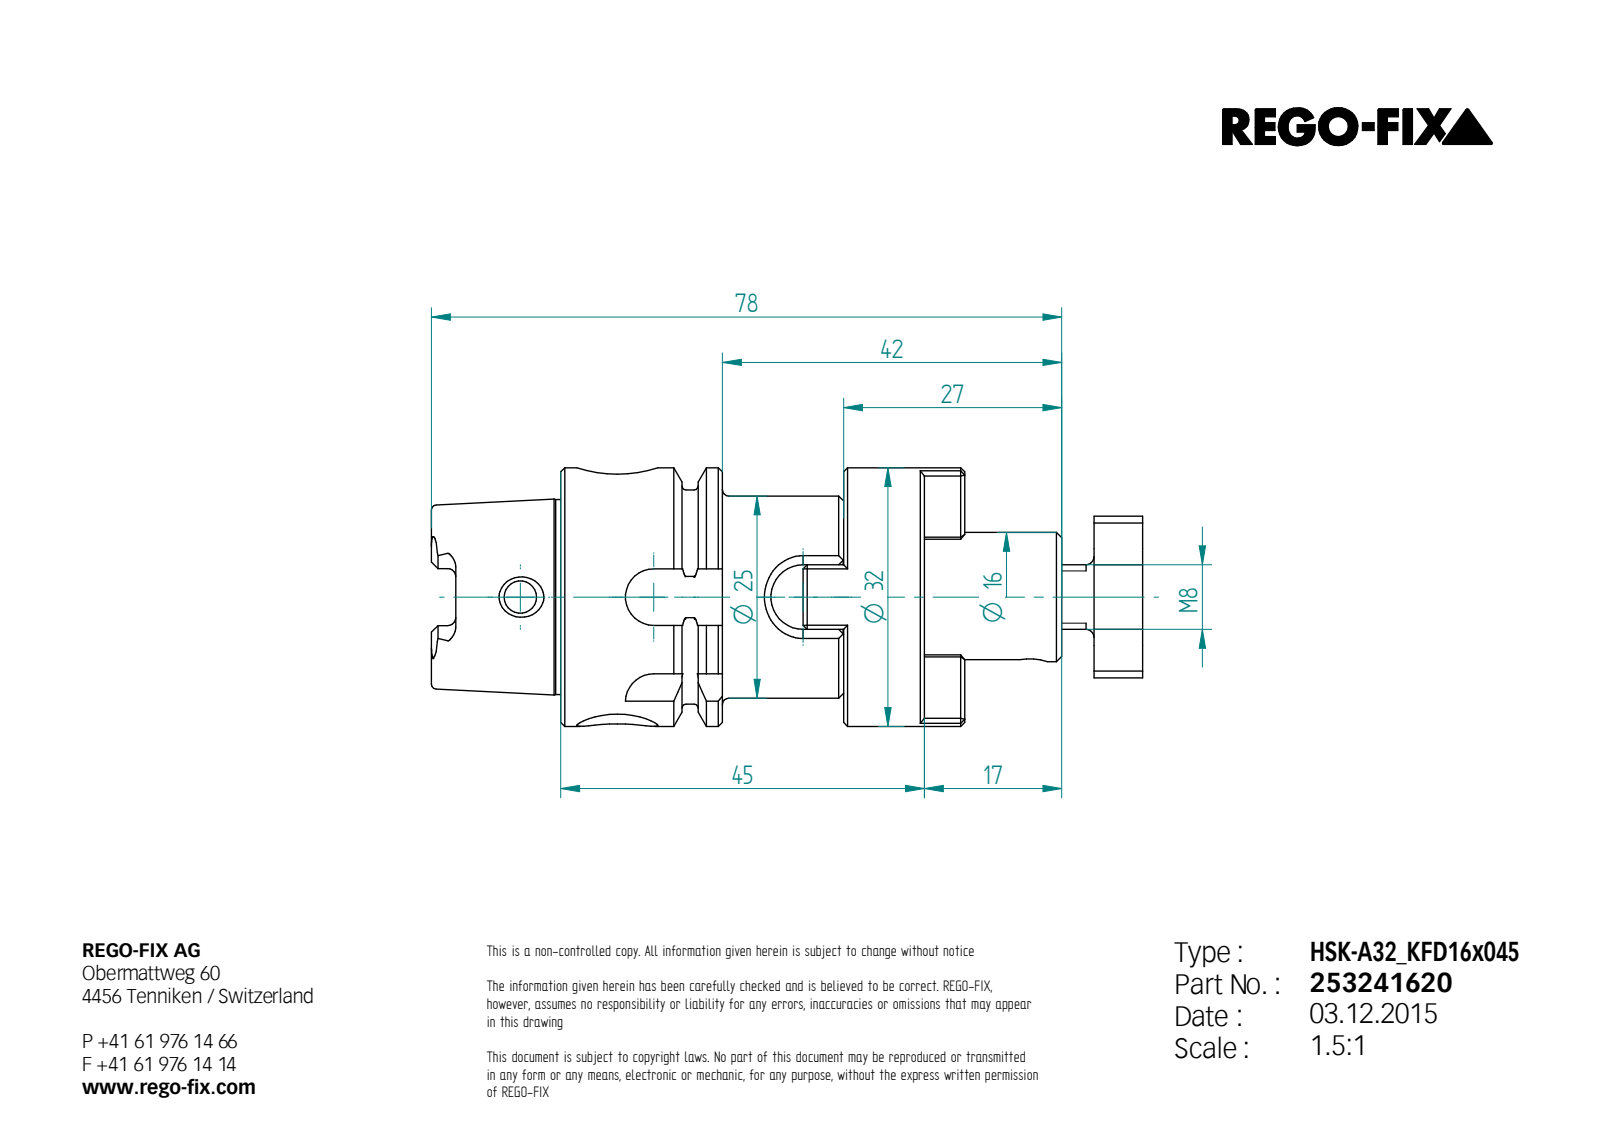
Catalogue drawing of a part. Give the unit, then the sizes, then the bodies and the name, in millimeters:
Units: millimetres
Overall size (bounding box): 88 × 32 × 32
Round holes (diameter × count): ⌀10 ×2, ⌀4 ×1, ⌀4.2 ×1, ⌀6.65 ×1, ⌀8.4 ×1, ⌀8.92 ×1, ⌀11 ×1, ⌀16 ×1, ⌀17 ×1, ⌀20.5 ×1
Round bosses / shafts (diameter × count): ⌀32 ×1, ⌀26.5 ×1, ⌀25 ×1, ⌀24.13 ×1, ⌀15.6 ×1, ⌀8 ×1
Partial cylindrical surfaces — rounded edges, fillets, slot ends (radius × count): R1 ×6, R2 ×6, R1.38 ×4, R3.5 ×4, R4 ×1, R10 ×1
Main face-to-face distances: 10, 15, 27, 8, 6, 37, 30, 17, 20, 5
Volume: 34 334 mm³ · Surface area: 14 841 mm²
Bodies: 3 solids, 264 faces (133 planar, 52 cylindrical, 79 other)
STEP written by: Unknown (AUTOMOTIVE_DESIGN)
